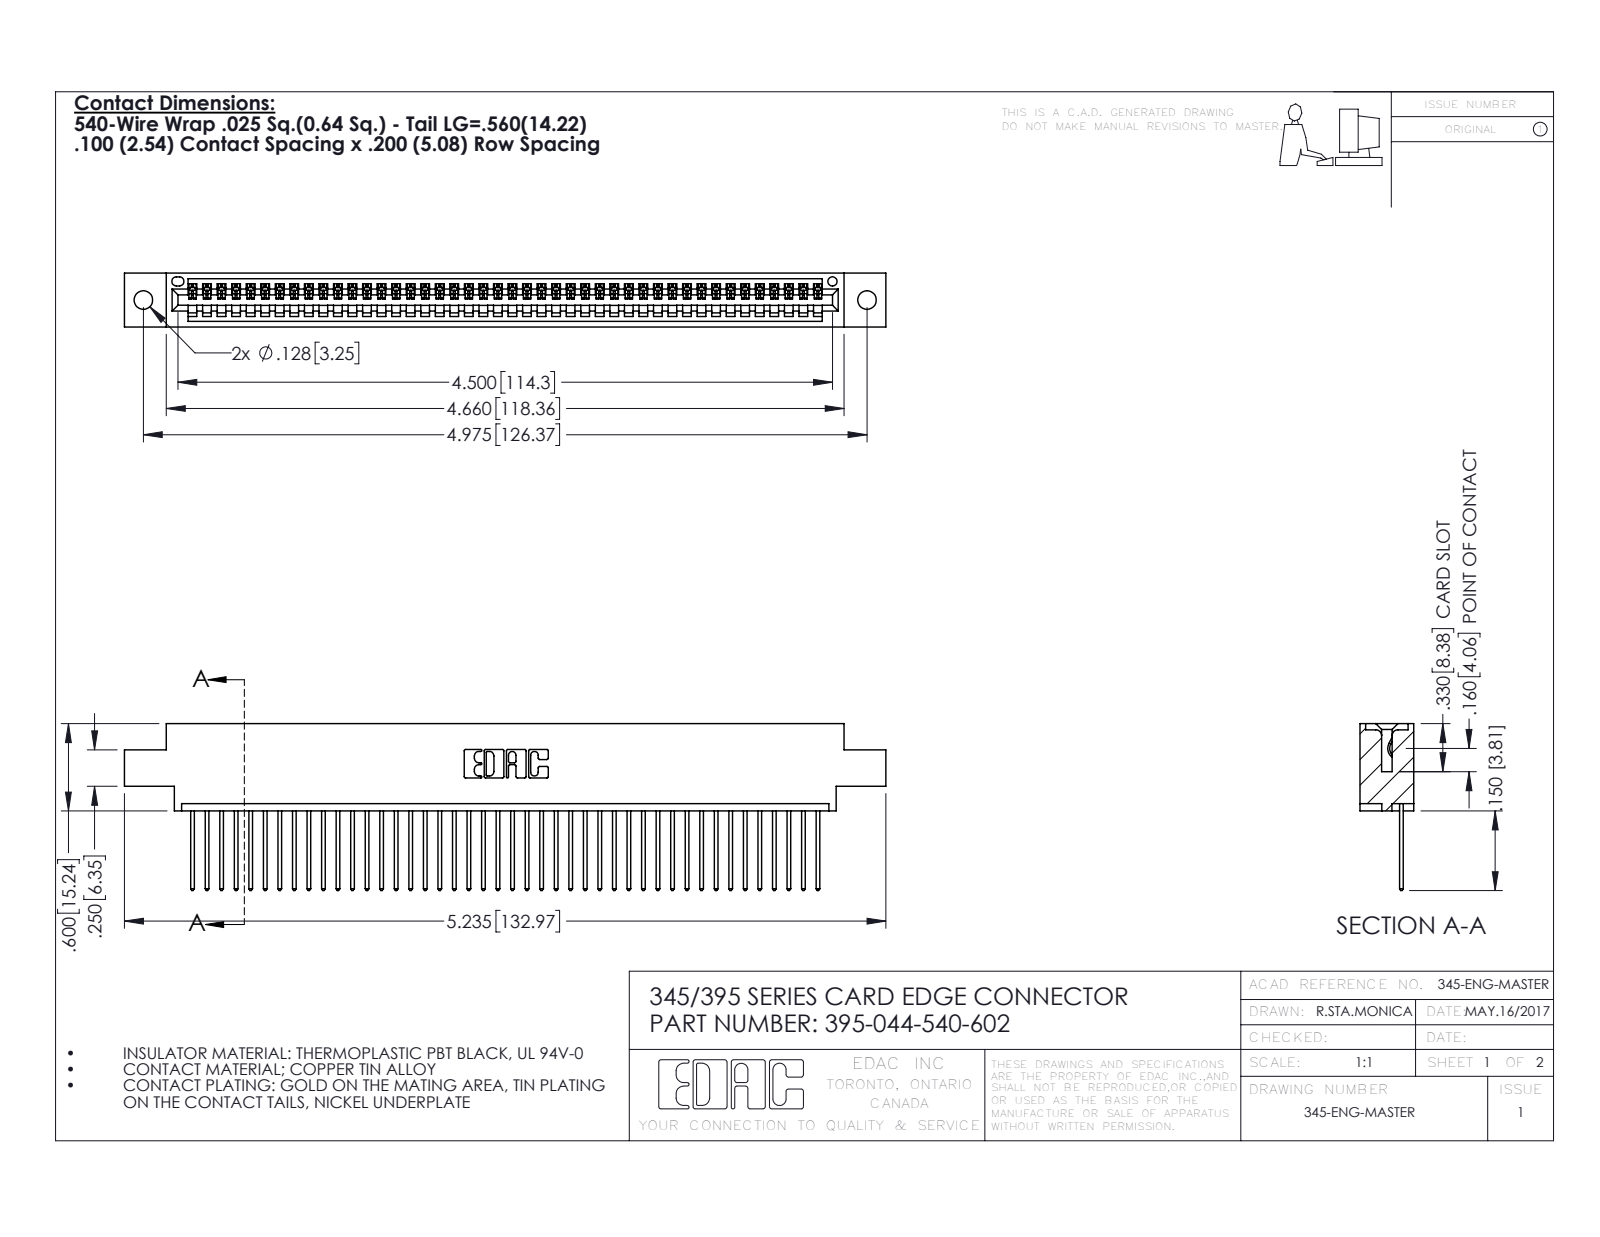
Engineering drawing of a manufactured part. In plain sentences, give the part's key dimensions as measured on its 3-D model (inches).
The part is named "345-292-001_345-293-140; 395-044-540-602; 345 Part_0.170 Offset - 0.128 Dia". Its 3-D file was written by "SolidWorks 2016 (CONFIG_CONTROL_DESIGN)". It is 45 solids with 2682 faces: 1844 planar, 838 cylindrical and 0 other. Overall it measures 5.235 by 1.147 by 0.37 inches. Its volume is 0.766 cubic inches and its surface area 26.34 square inches. Round holes: 2 of diameter 0.128, 1 of diameter 0.064. Partial cylindrical surfaces (rounded edges, fillets, slot ends): 88 of radius 0.006, 88 of radius 0.01, 22 of radius 0.01, 6 of radius 0.007, 6 of radius 0.031, 3 of radius 0.026, 2 of radius 0.031, 2 of radius 0.04. The main face-to-face distances are 0.298, 0.072, 0.37, 0.098, 0.272, 0.025, 0.2, 0.225, 0.175, 0.149. The hole center spacings are 0.27, 4.739, 4.975.
